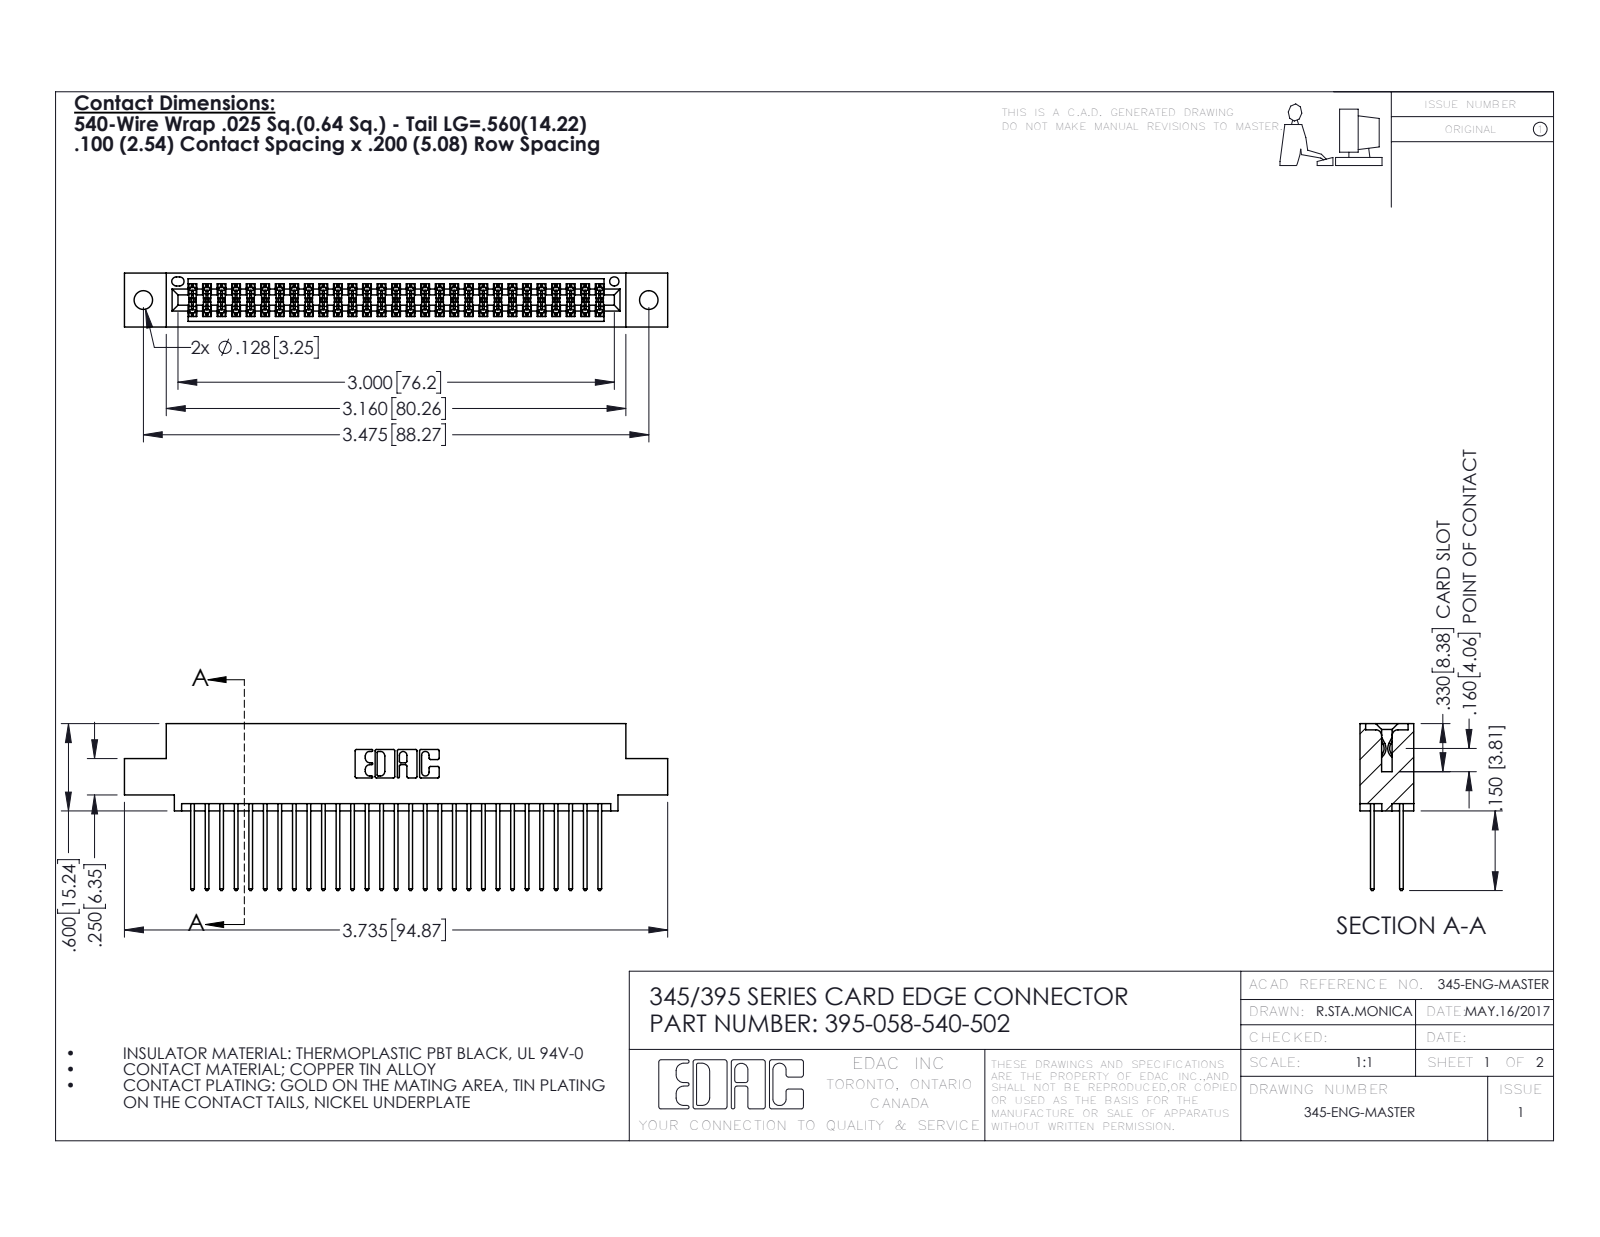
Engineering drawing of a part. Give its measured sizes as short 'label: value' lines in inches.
name: 345 Part_0.110 Offset - 0.128 Dia; 345-292-001_345-293-140; 395-058-540-502
written by: SolidWorks 2016 (CONFIG_CONTROL_DESIGN)
unit: in
bodies: 59 solids, 3030 faces (1998 planar, 1032 cylindrical, 0 other)
size: 3.735 × 1.147 × 0.37
volume: 0.562 in³; area: 22 in²
holes: 2× ⌀0.128, 1× ⌀0.064
rounds: 87× R0.006, 58× R0.01, 22× R0.01, 6× R0.007, 6× R0.031, 3× R0.026, 2× R0.014, 2× R0.019
face distances: 0.298, 0.072, 0.2, 0.098, 0.272, 0.025, 0.37, 0.225, 0.175, 0.149
hole spacings: 0.27, 3.24, 3.475
